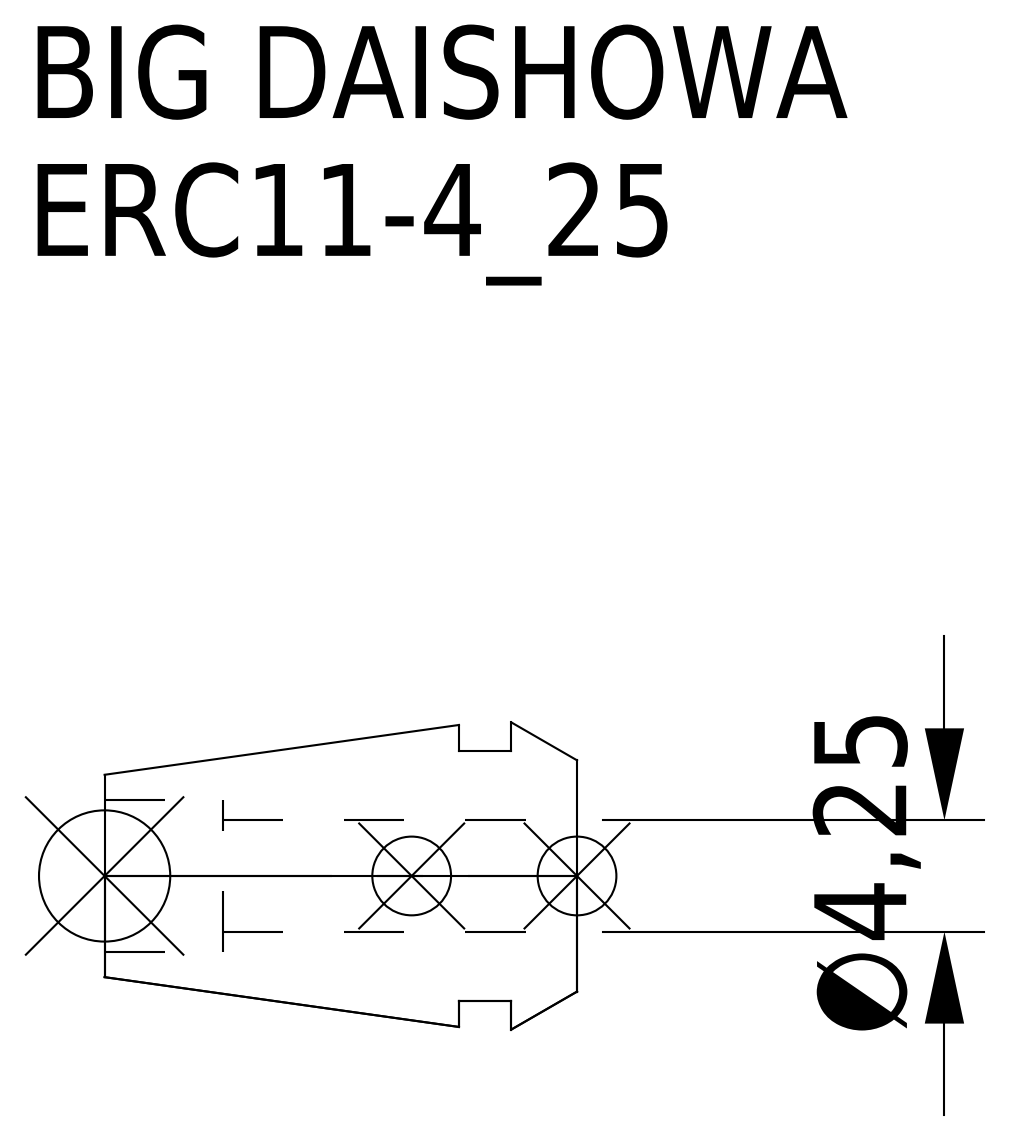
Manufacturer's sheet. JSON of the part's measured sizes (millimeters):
{"part_name": "ERC11-4_25", "step_written_by": "CREO PARAMETRIC BY PTC INC, 2016380 (AUTOMOTIVE_DESIGN)", "units": "millimeters", "bodies": {"solids": 1, "faces": 15, "planar": 5, "cylindrical": 6, "other": 4}, "overall_size": [18, 11.7, 11.7], "volume_mm3": 1031, "surface_area_mm2": 976, "round_holes": [[4.25, 1], [5.8, 1]], "round_bosses_or_shafts": [[9.5, 1]], "face_to_face_distances": [4.5, 2.5, 2, 13.5, 18, 15.5, 11, 9]}
